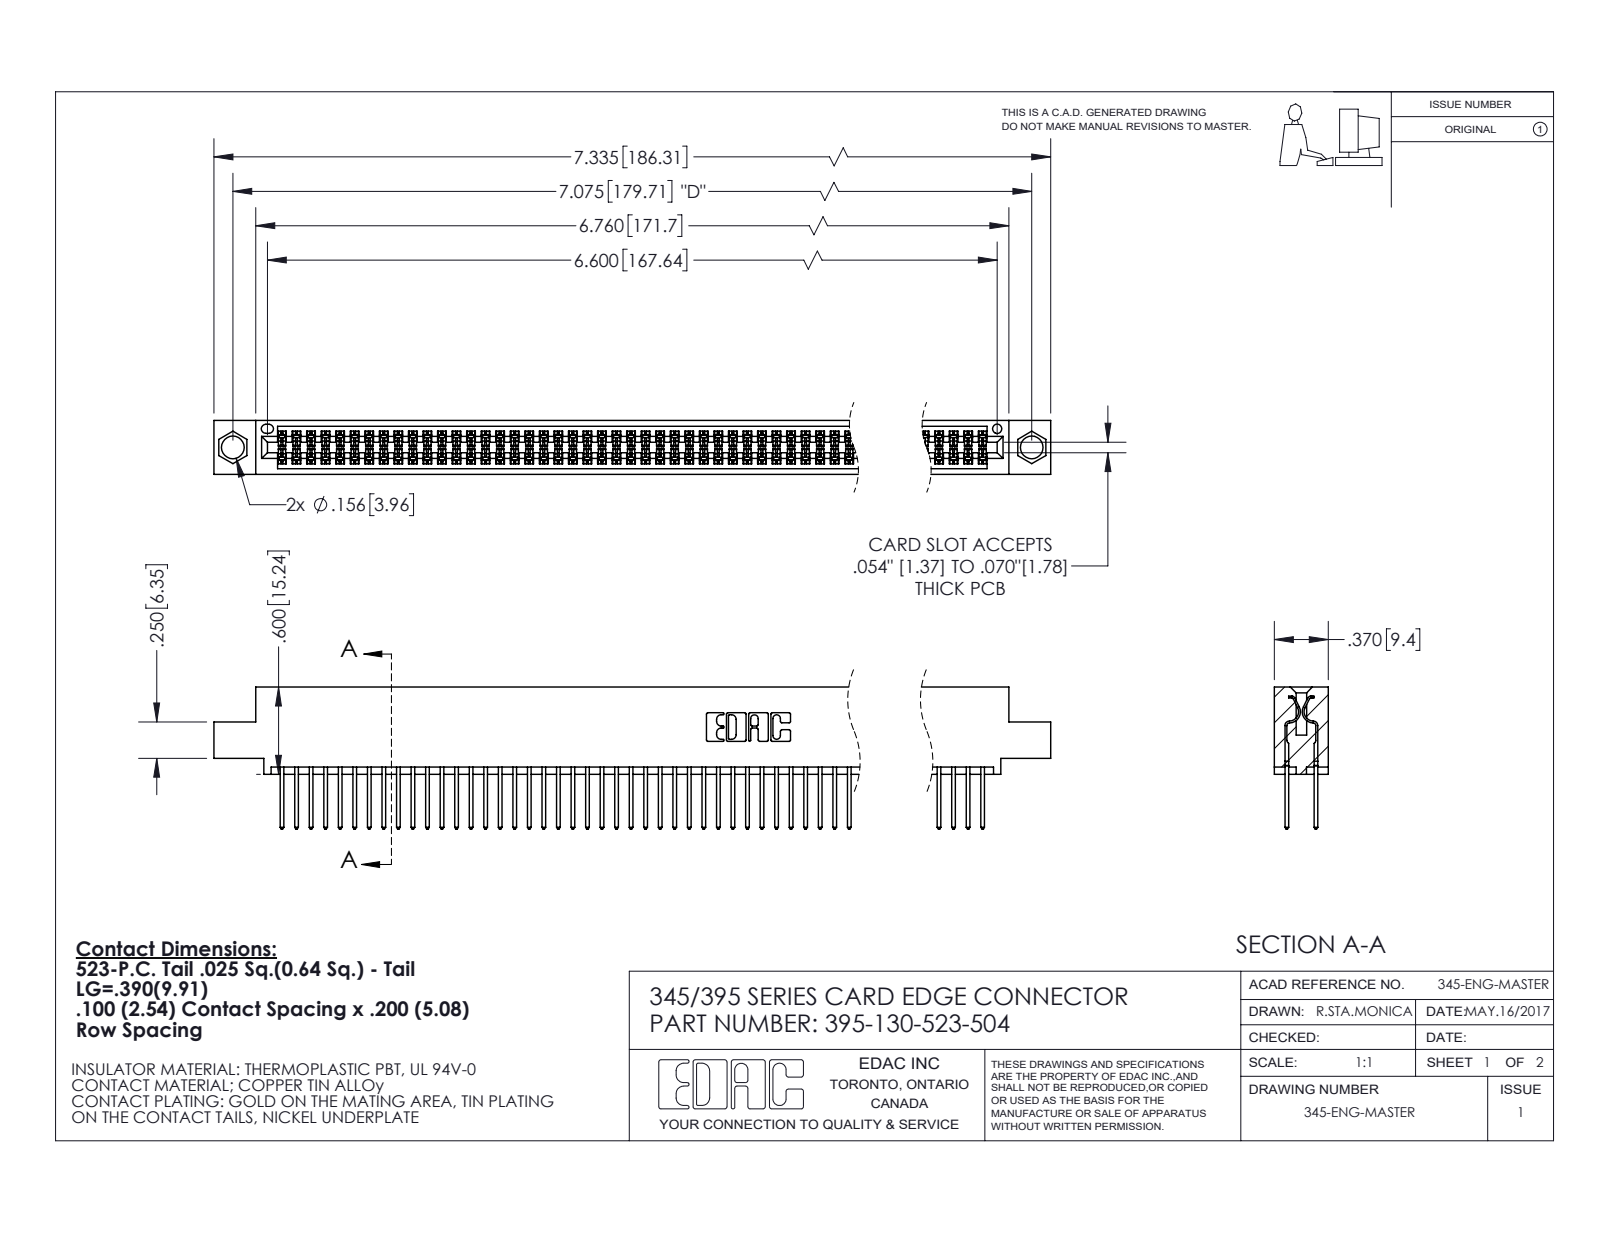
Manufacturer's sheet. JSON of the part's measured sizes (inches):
{"part_name": "345 Part_0.110 Offset - 0.156 Dia-TI; 345-292-001_345-293-123; 395-130-523-504", "step_written_by": "SolidWorks 2020 (CONFIG_CONTROL_DESIGN)", "units": "inches", "bodies": {"solids": 131, "faces": 6644, "planar": 4388, "cylindrical": 2256, "other": 0}, "overall_size": [7.335, 0.977, 0.37], "volume_in3": 1.123, "surface_area_in2": 44.61, "round_holes": [[0.156, 2], [0.064, 1]], "partial_cylinders_radius": [[0.006, 195], [0.01, 130], [0.01, 22], [0.007, 6], [0.031, 6], [0.026, 3], [0.014, 2], [0.019, 2]], "face_to_face_distances": [0.072, 0.298, 0.2, 0.098, 0.272, 0.025, 0.37, 0.225, 0.175, 0.149], "hole_center_spacings": [0.27, 6.839, 7.075]}
